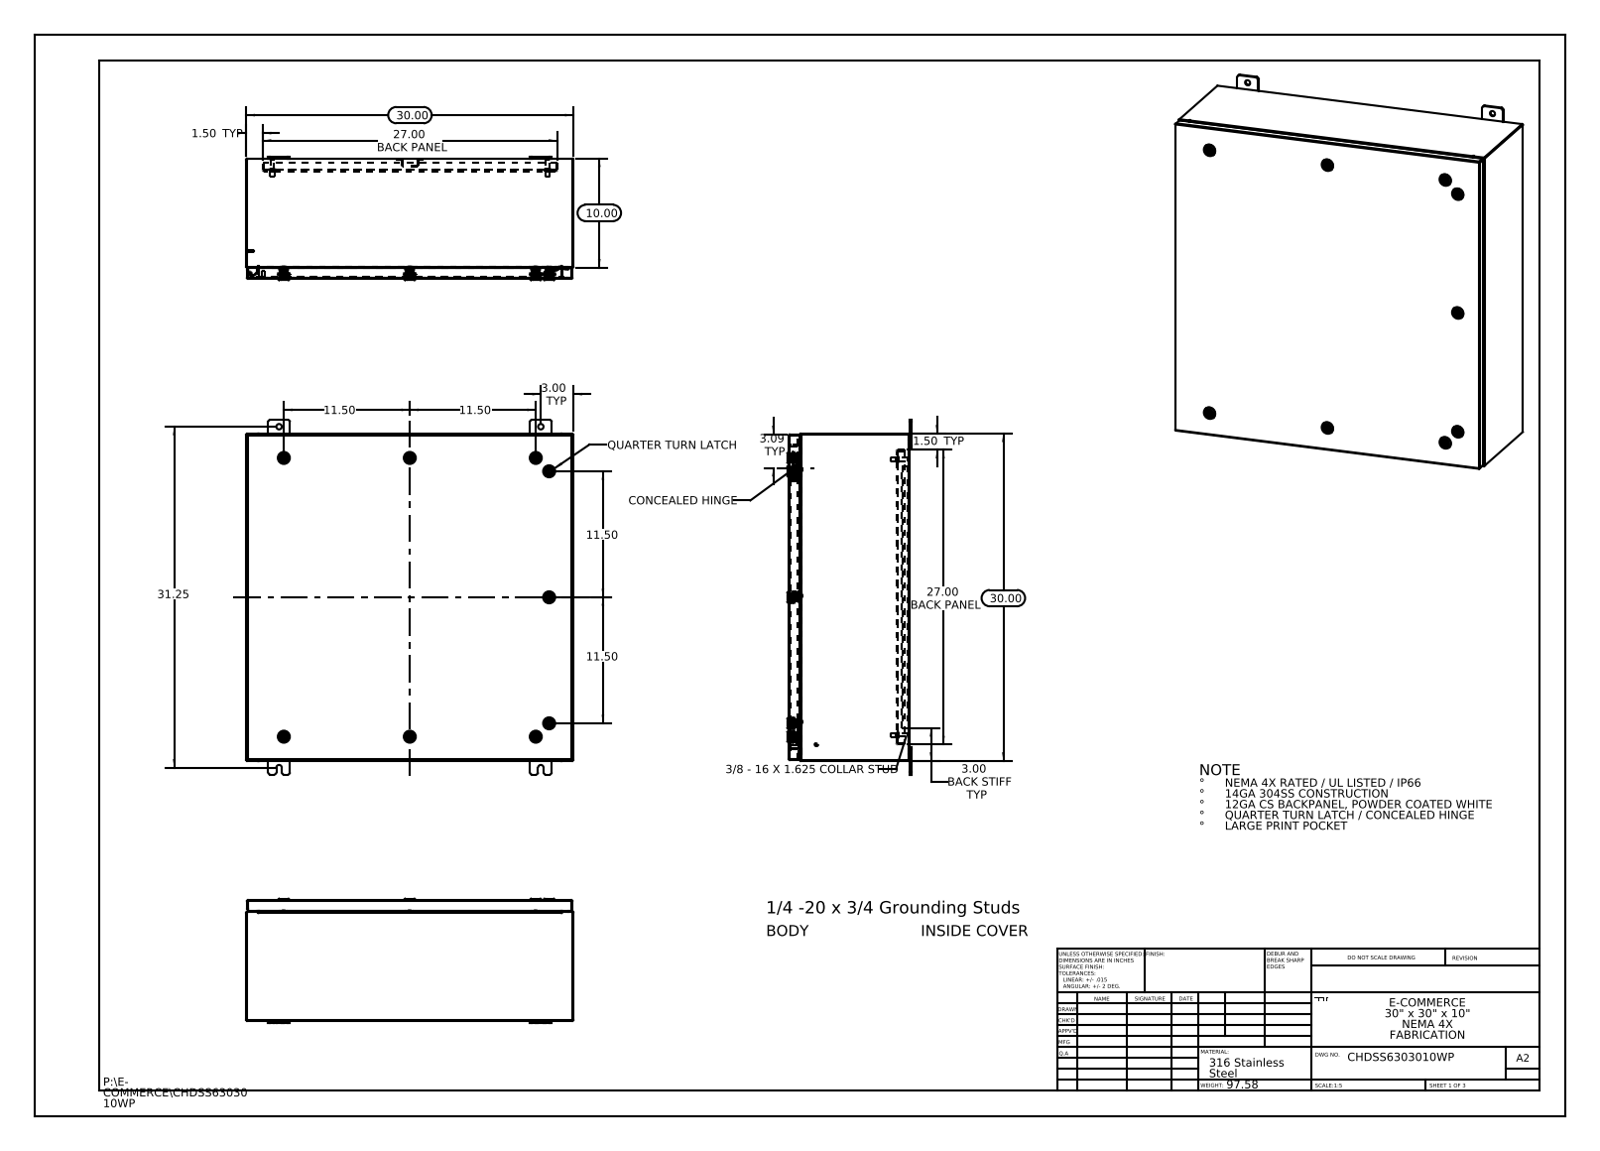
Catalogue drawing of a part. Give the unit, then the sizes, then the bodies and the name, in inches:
Units: inches
Overall size (bounding box): 32.5 × 30 × 11.356
Round holes (diameter × count): ⌀0.197 ×9, ⌀0.394 ×9, ⌀0.4 ×9, ⌀0.63 ×9, ⌀0.787 ×9, ⌀0.5 ×8, ⌀0.136 ×2, ⌀0.211 ×1
Round bosses / shafts (diameter × count): ⌀0.236 ×11, ⌀1.102 ×9, ⌀0.78 ×9, ⌀0.626 ×9, ⌀0.61 ×9, ⌀0.531 ×9, ⌀0.392 ×9, ⌀0.114 ×9
Partial cylindrical surfaces — rounded edges, fillets, slot ends (radius × count): R0.006 ×297, R0.118 ×297, R0.028 ×108, R0.02 ×36, R0.197 ×36, R0.013 ×26, R0.19 ×24, R0.088 ×22
Main face-to-face distances: 0.075, 29.925, 0.074, 11.01, 10.935, 10.936, 10.861, 0.104, 1, 1.075
Hole centre spacings: 11.55, 28.039, 12.834, 23.1, 24.356, 25.55, 1.858, 24
Volume: 346.6 in³ · Surface area: 8 622 in²
Bodies: 72 solids, 7862 faces (2246 planar, 2442 cylindrical, 3174 other)
Part name (STEP PRODUCT): Housing-211301-IB-Industrilas_Housing-211301-IB-Industrilas; CHDSS6303010WP Mounting Feet; Concealed Hinge enclosure side; Quarter-20 CD Stud (+8 more)
STEP written by: SolidWorks 2013 (CONFIG_CONTROL_DESIGN)
